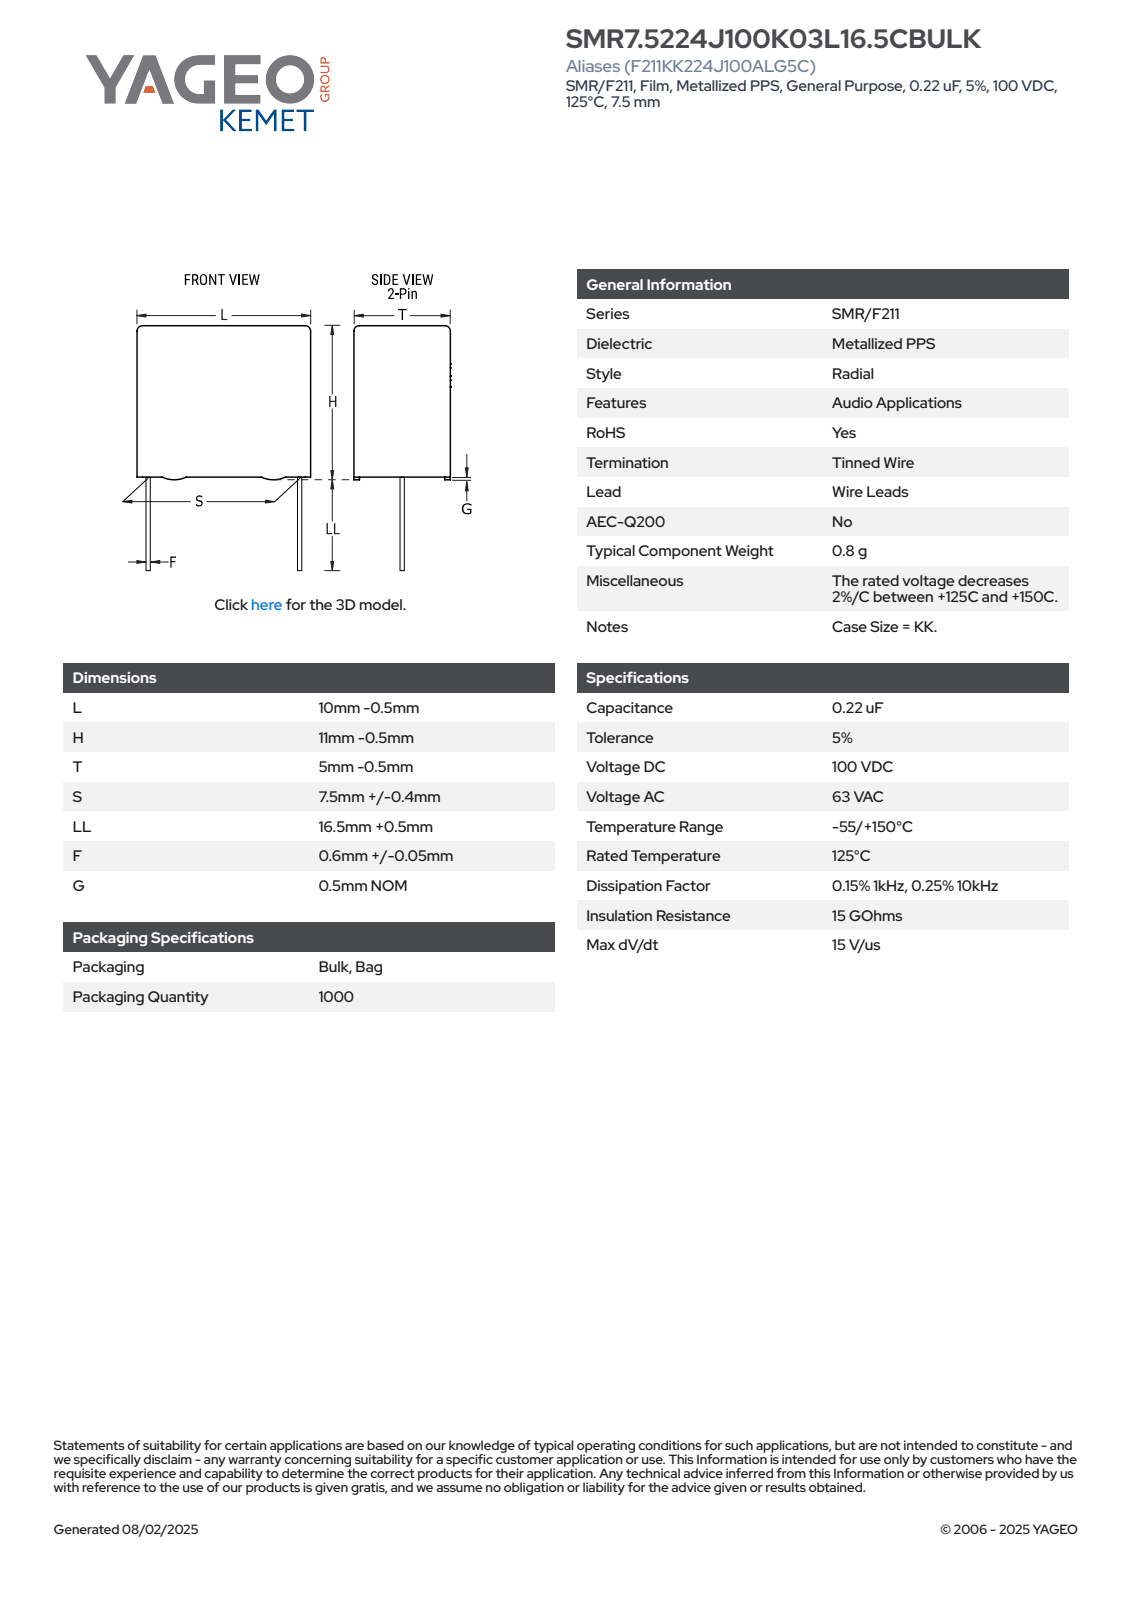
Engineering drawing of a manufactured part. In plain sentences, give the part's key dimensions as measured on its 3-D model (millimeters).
The part is named "CFR_RBG_10X11X5_L9.5H10.5T4.5S7.5LL17F0.65G0.5". Its 3-D file was written by "SolidWorks 2021 (AUTOMOTIVE_DESIGN)". It is 4 solids with 89 faces: 81 planar, 8 cylindrical and 0 other. Overall it measures 27.5 by 9.5 by 4.5 millimeters. Its volume is 439 cubic millimeters and its surface area 448 square millimeters. Round bosses or shafts: 2 of diameter 0.65. Partial cylindrical surfaces (rounded edges, fillets, slot ends): 4 of radius 0.5. The main face-to-face distances are 4.5, 9.5, 10, 4.24, 3.98, 0.5, 10.5, 17, 17.5, 27.5.
